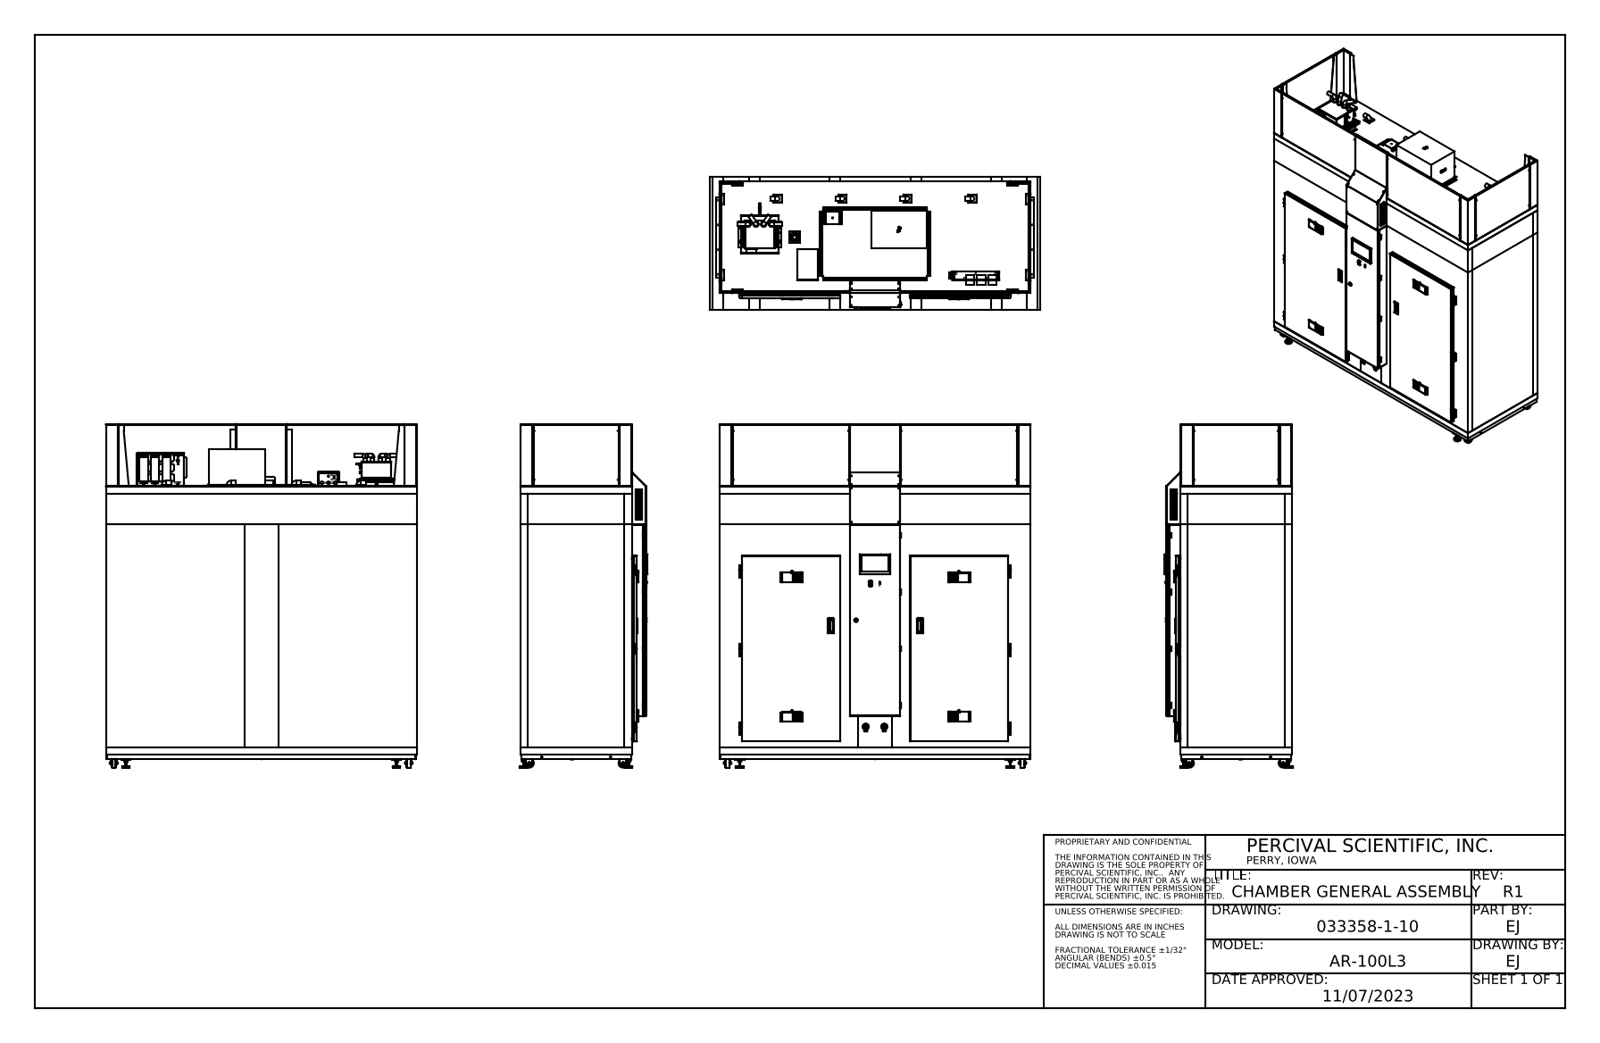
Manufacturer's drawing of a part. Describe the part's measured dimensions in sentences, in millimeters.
The part is named "2005-4C-30E; YHP-002; 2005-4B-60-1; HST-002 (+8 more)". Its 3-D file was written by "SolidWorks 2023 (AUTOMOTIVE_DESIGN)". It is 1236 solids with 119147 faces: 47597 planar, 10342 cylindrical and 61208 other. Overall it measures 2819.5 by 2552.7 by 1049.7 millimeters. Its volume is 999 700 000 cubic millimeters and its surface area 150 900 000 square millimeters. Round holes: 422 of diameter 3.2, 346 of diameter 4, 170 of diameter 3.2, 128 of diameter 3.7, 128 of diameter 6.4, 28 of diameter 5.6, 28 of diameter 8, 28 of diameter 12.7, 26 of diameter 7.4, 24 of diameter 7.1, 20 of diameter 4, 19 of diameter 4.7. Round bosses or shafts: 128 of diameter 8.6, 128 of diameter 7.5, 128 of diameter 6.3, 12 of diameter 7.9, 12 of diameter 6.6, 12 of diameter 5.4, 8 of diameter 6.4, 8 of diameter 4.9. Partial cylindrical surfaces (rounded edges, fillets, slot ends): 1261 of radius 1.6, 256 of radius 2.8, 128 of radius 0.2, 115 of radius 2.3, 88 of radius 2.4, 88 of radius 3.6, 55 of radius 1.6, 50 of radius 6.4. The main face-to-face distances are 50.8, 0.8, 863.6, 812.8, 914.4, 812.7, 2152.7, 101.6, 0.8, 0.7. The hole center spacings are 152.4, 304.8, 1175.9, 457.2, 1205.2, 609.6, 1252.4, 1315.7.
